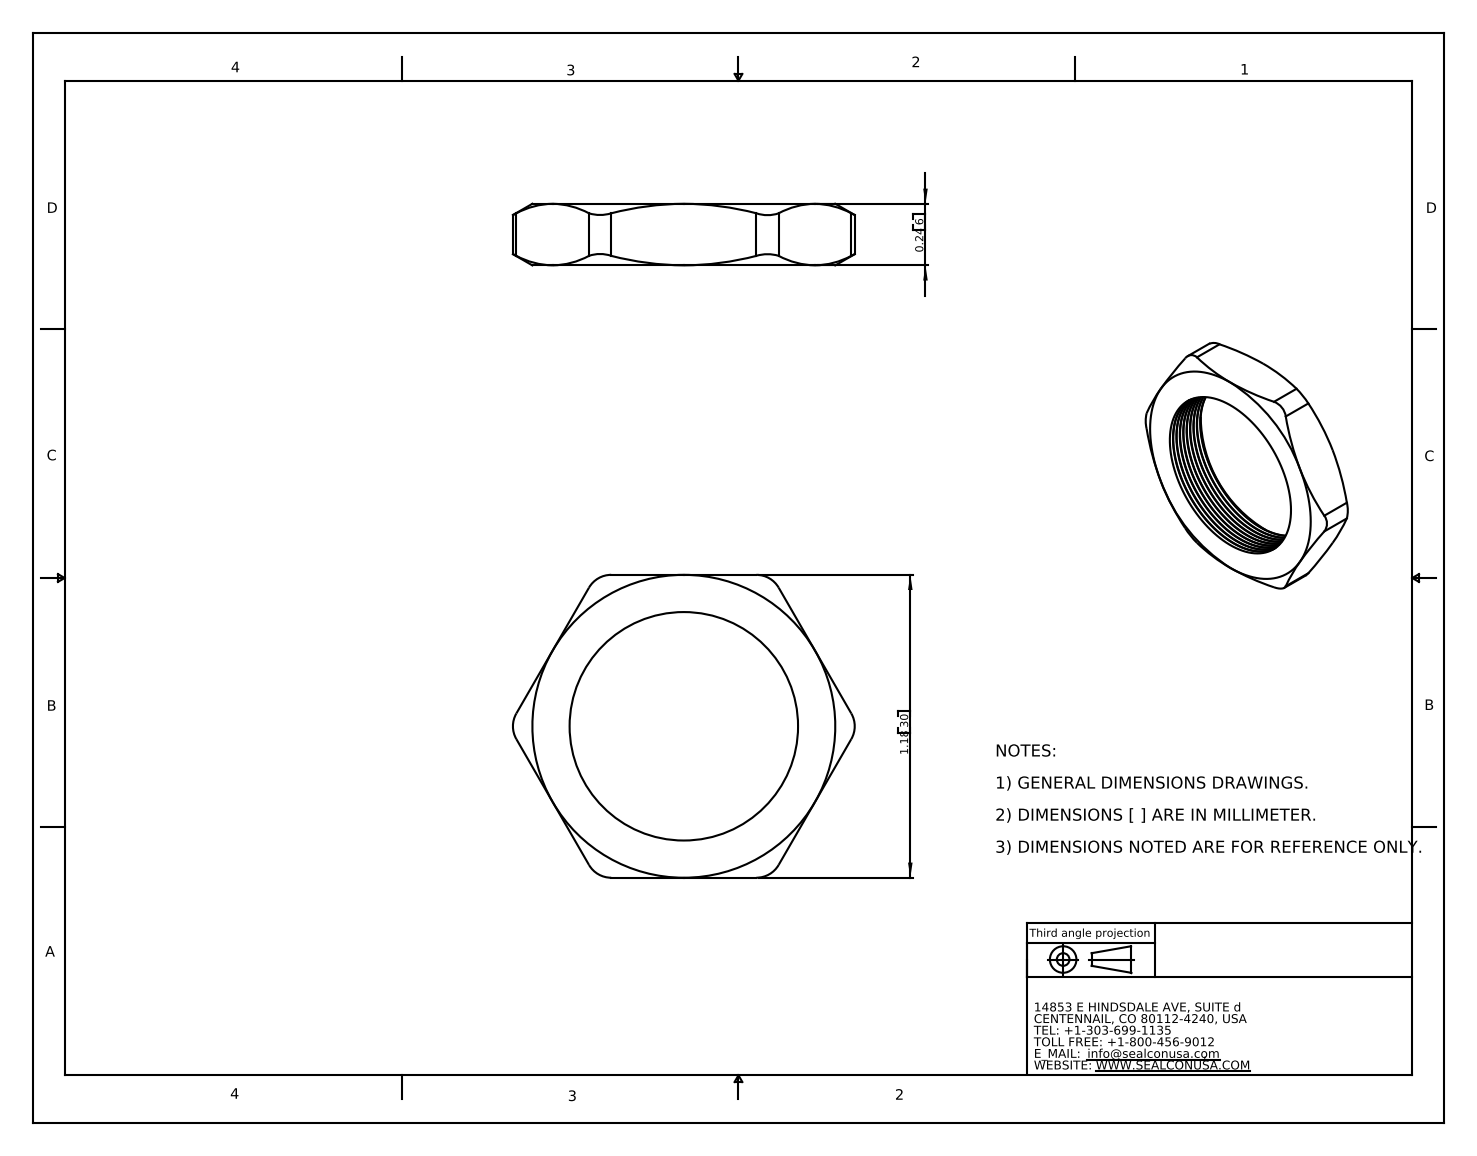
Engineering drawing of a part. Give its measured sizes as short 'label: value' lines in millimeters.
name: NP-16
written by: SolidWorks 2007 (CONFIG_CONTROL_DESIGN)
unit: mm
bodies: 1 solid, 87 faces (8 planar, 25 cylindrical, 54 other)
size: 33.8 × 30 × 6.1
volume: 2 130 mm³; area: 2 132 mm²
holes: 1× ⌀22.6
rounds: 6× R2.5
face distances: 6.1, 30
